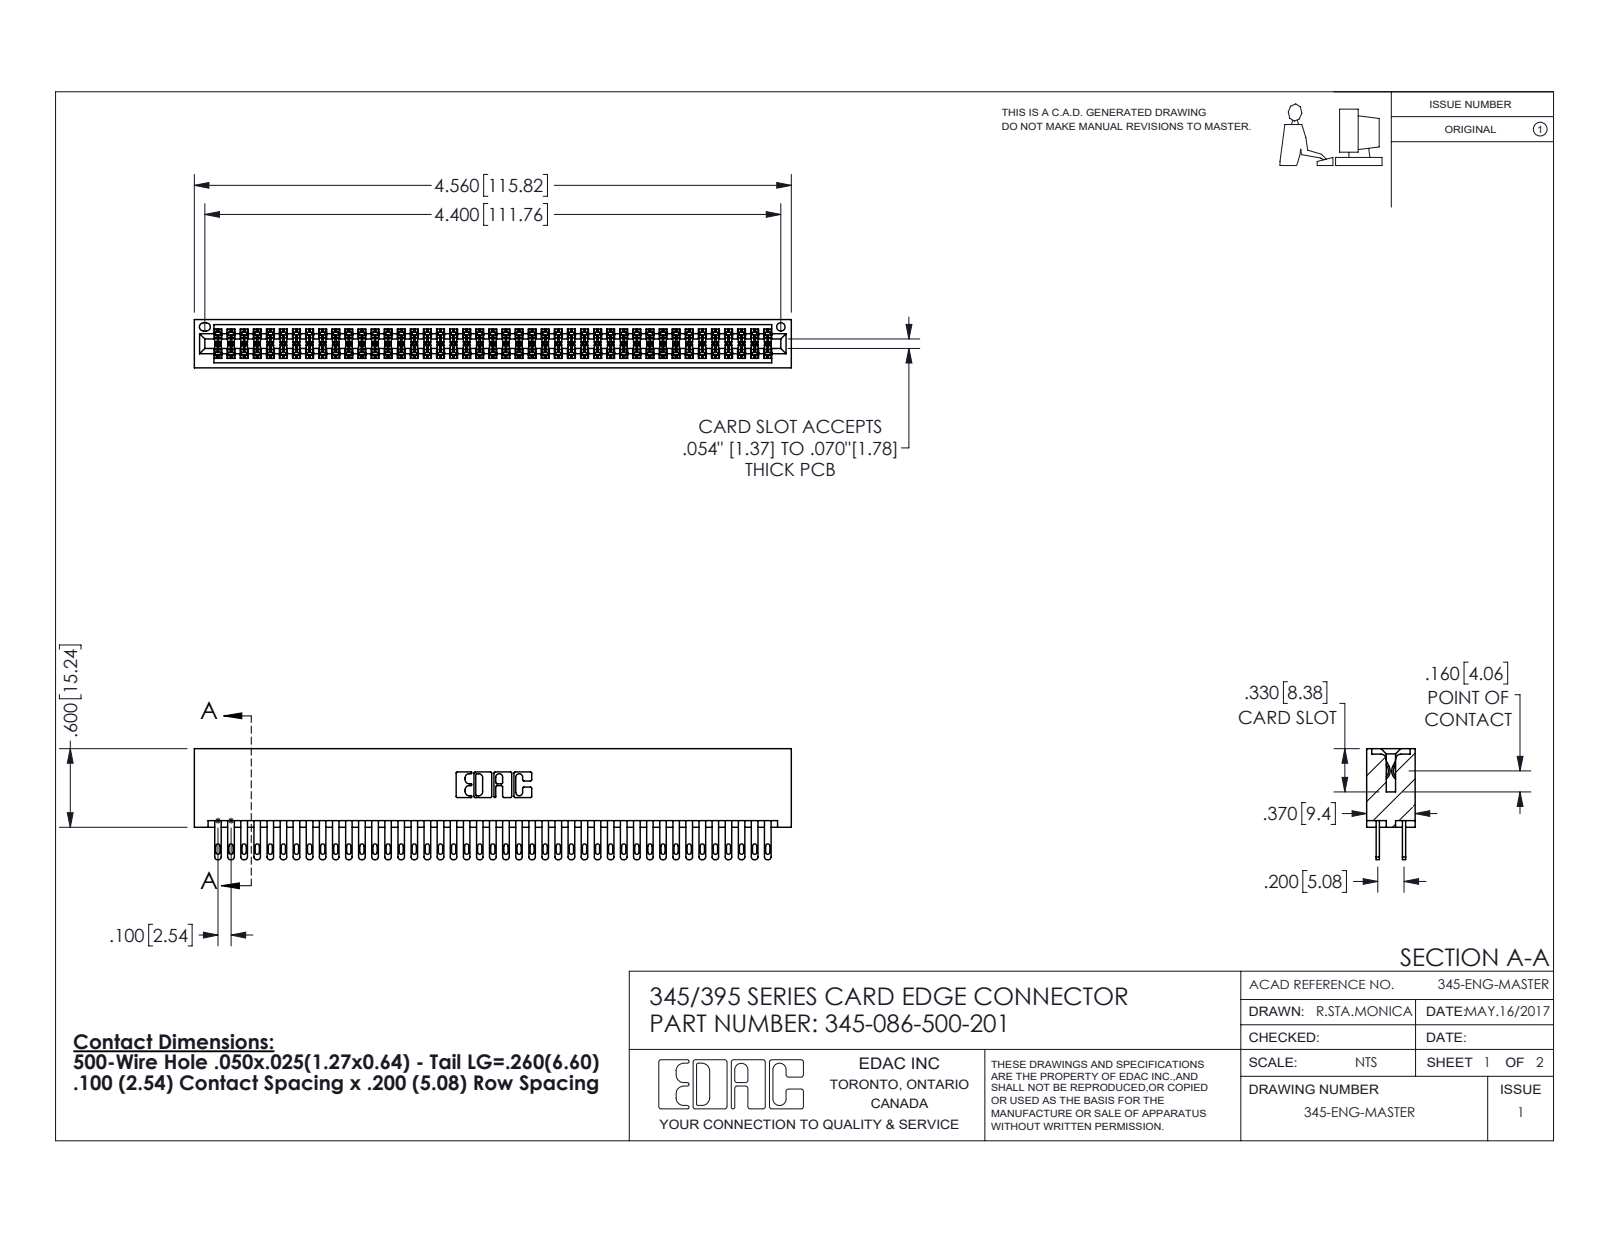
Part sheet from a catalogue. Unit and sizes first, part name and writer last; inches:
Units: inches
Overall size (bounding box): 4.56 × 0.847 × 0.37
Round holes (diameter × count): ⌀0.064 ×1
Partial cylindrical surfaces — rounded edges, fillets, slot ends (radius × count): R0.006 ×129, R0.016 ×86, R0.02 ×86, R0.01 ×22, R0.007 ×6, R0.031 ×6, R0.026 ×3, R0.014 ×2
Main face-to-face distances: 0.298, 0.072, 0.2, 0.098, 0.272, 0.025, 0.37, 0.225, 0.175, 0.149
Volume: 0.741 in³ · Surface area: 29.67 in²
Bodies: 87 solids, 4074 faces (2398 planar, 1676 cylindrical, 0 other)
Part name (STEP PRODUCT): 345-086-500-201; 345-292-001_345-293-100; 345 Part_No Mounting Lugs
STEP written by: SolidWorks 2016 (CONFIG_CONTROL_DESIGN)
